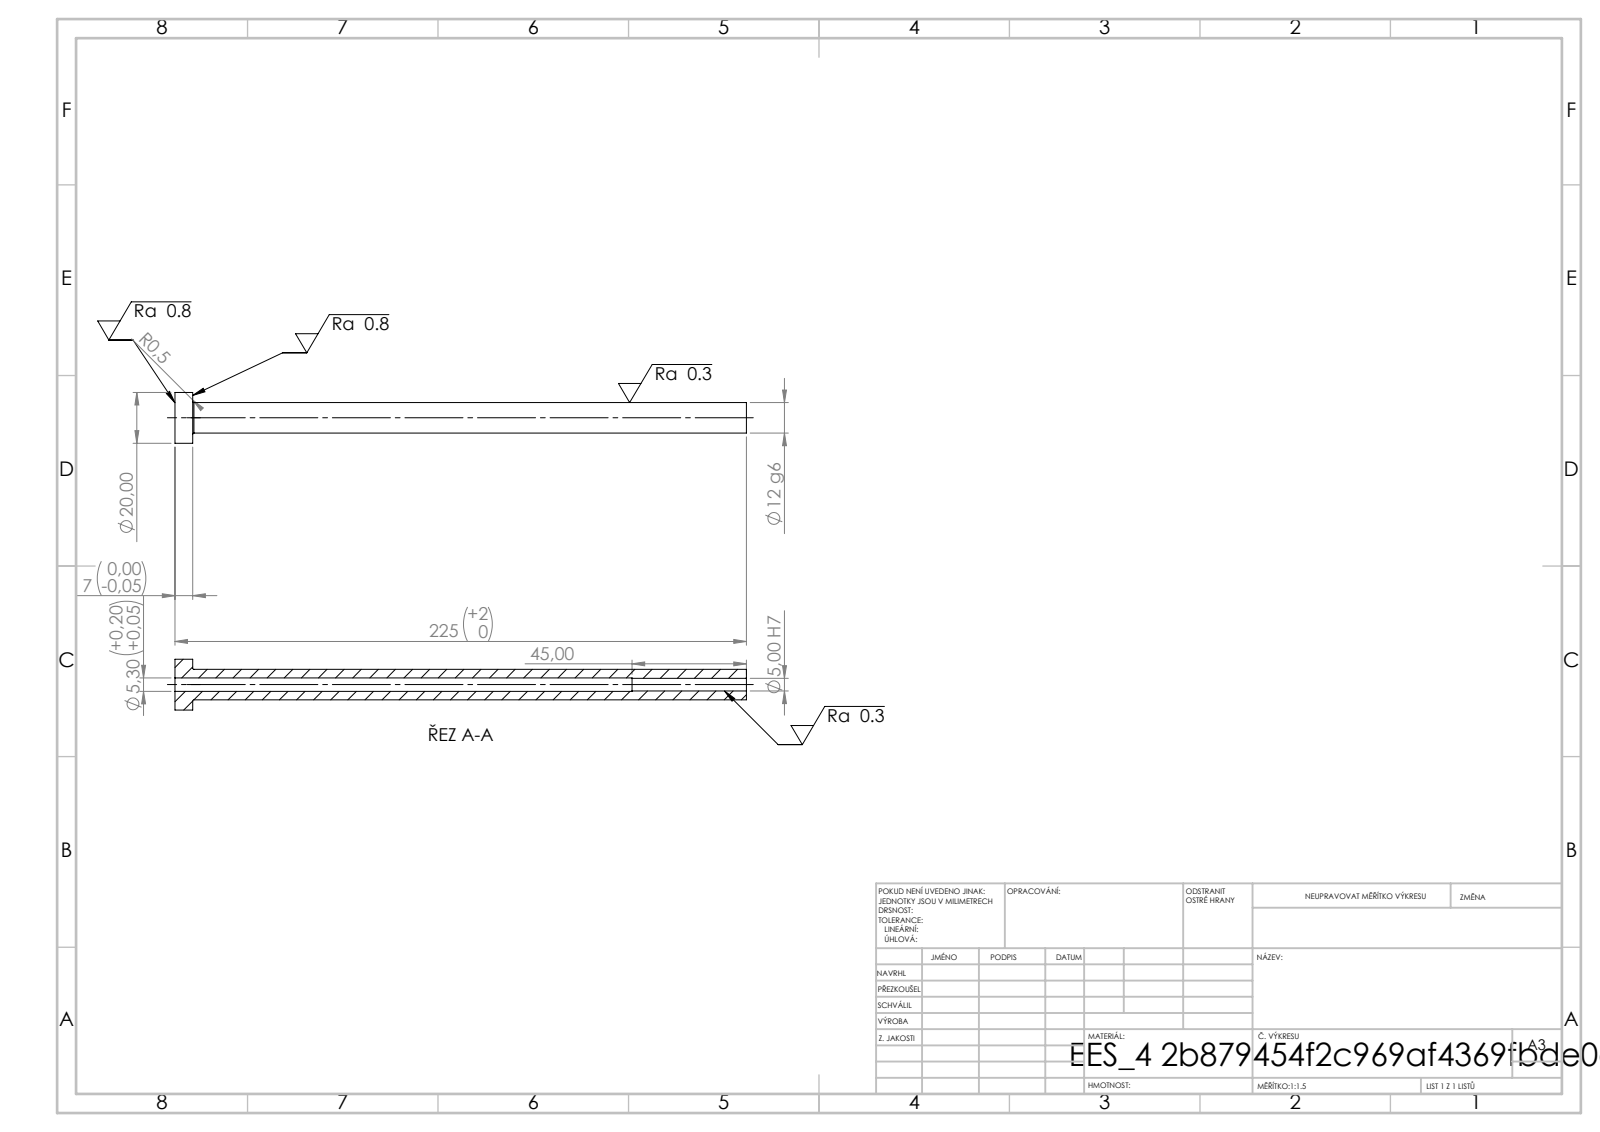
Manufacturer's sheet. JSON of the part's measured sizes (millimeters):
{"step_written_by": "SolidWorks 2019 (CONFIG_CONTROL_DESIGN)", "units": "millimeters", "bodies": {"solids": 1, "faces": 14, "planar": 4, "cylindrical": 8, "other": 2}, "overall_size": [225, 20, 20], "volume_mm3": 22002, "surface_area_mm2": 12943, "round_holes": [[5, 1], [5.3, 1]], "round_bosses_or_shafts": [[20, 1], [12, 1]], "face_to_face_distances": [7, 225, 218, 180, 173, 45]}
